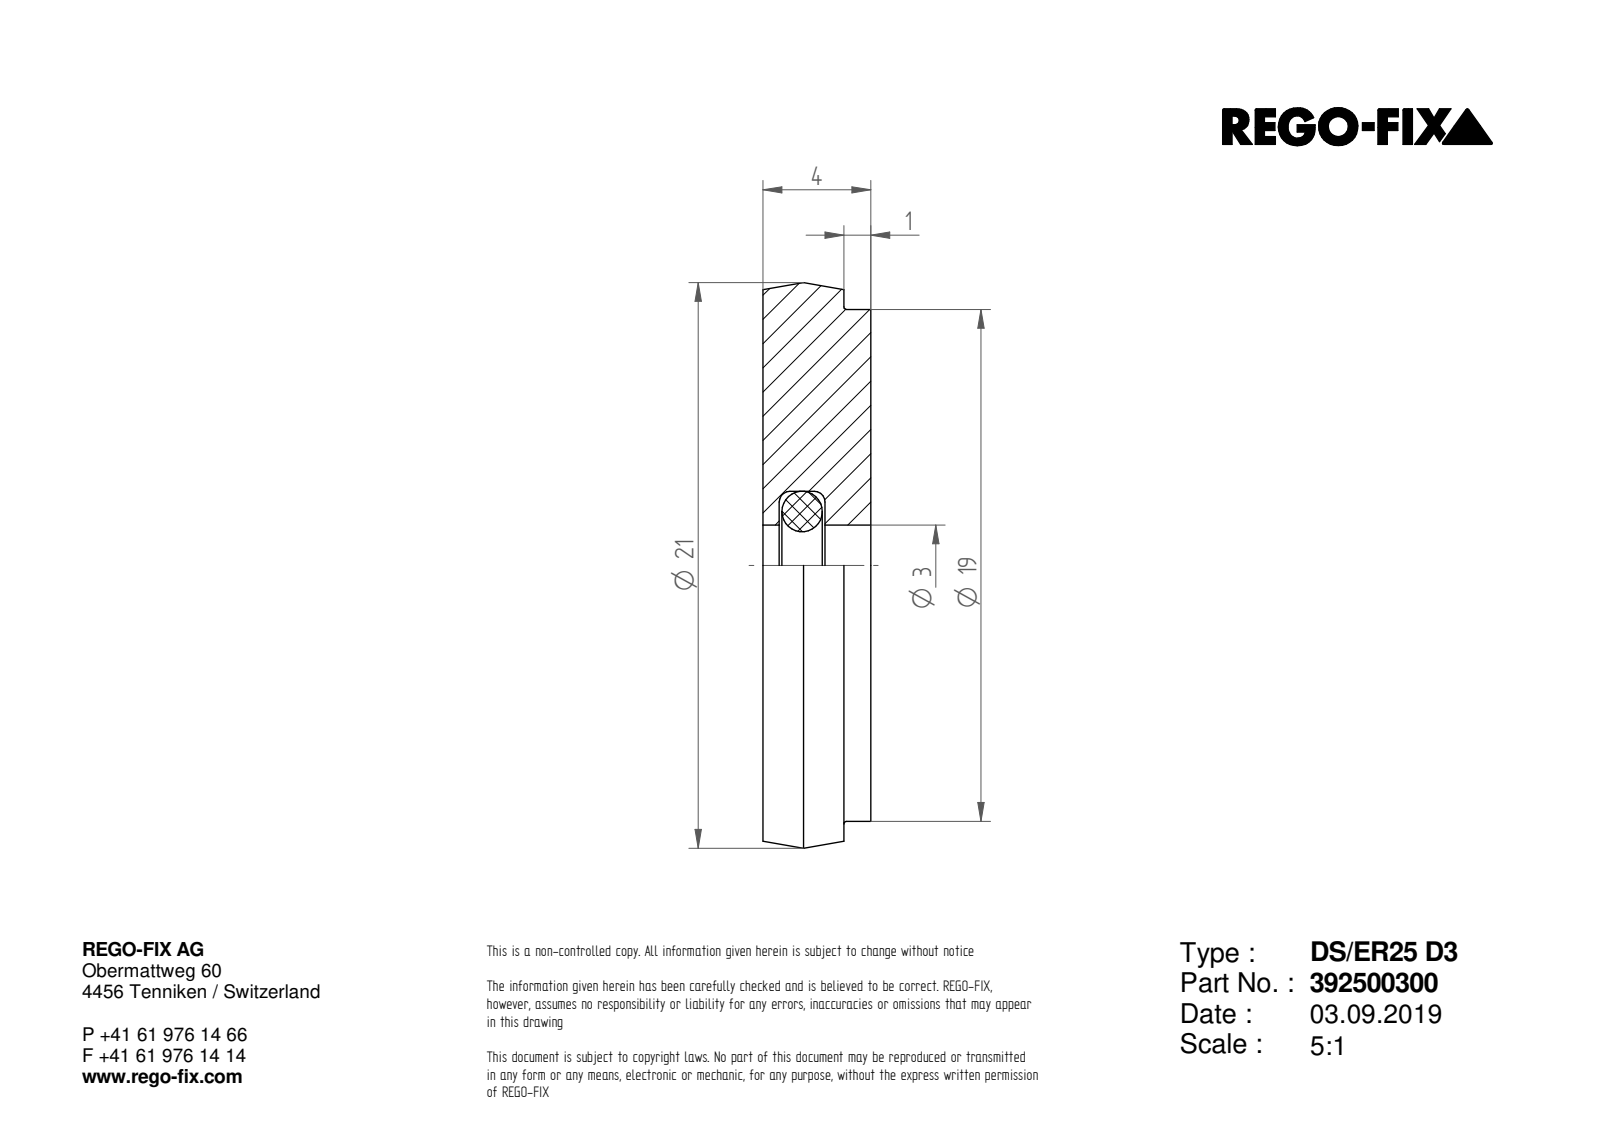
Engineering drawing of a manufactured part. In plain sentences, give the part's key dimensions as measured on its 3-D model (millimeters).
The part is named "NOCUT". Its 3-D file was written by "SIEMENS PLM Software Solid Edge ST10 (AUTOMOTIVE_DESIGN)". It is 1 solid with 7 faces: 3 planar, 3 cylindrical and 1 other. Overall it measures 21 by 21 by 4 millimeters. Its volume is 1 294 cubic millimeters and its surface area 971 square millimeters. Round holes: 1 of diameter 3. Round bosses or shafts: 1 of diameter 21, 1 of diameter 19. The main face-to-face distances are 4, 1, 3.
